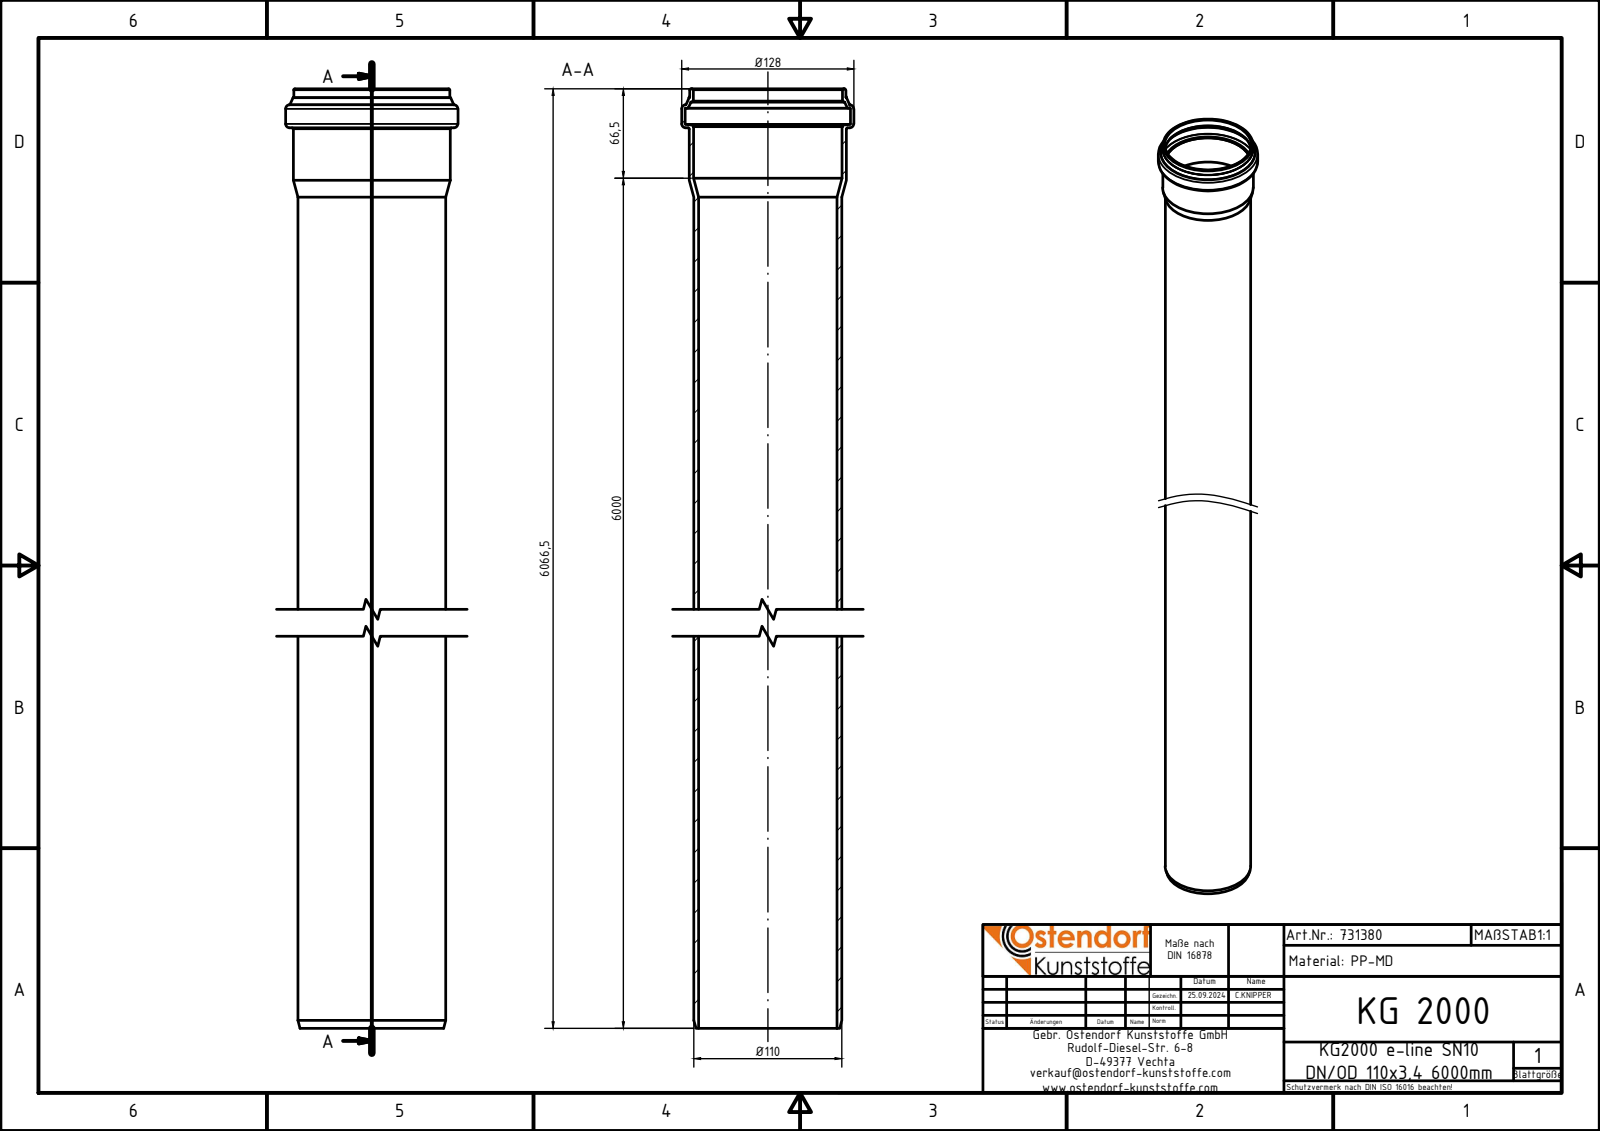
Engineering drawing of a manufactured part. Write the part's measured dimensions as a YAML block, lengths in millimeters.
part_name: "731380z"
step_written_by: "Autodesk Inventor 2024 (AUTOMOTIVE_DESIGN)"
units: millimeters
bodies: {solids: 1, faces: 36, planar: 5, cylindrical: 9, other: 22}
overall_size: [6066.5, 128, 128]
volume: 7141000
surface_area: 4071000
round_holes:
  - {diameter: 102.96, count: 1}
  - {diameter: 110.5, count: 1}
  - {diameter: 110.9, count: 1}
  - {diameter: 122.8, count: 1}
round_bosses_or_shafts:
  - {diameter: 128, count: 1}
  - {diameter: 116.7, count: 1}
  - {diameter: 116.1, count: 1}
  - {diameter: 110, count: 1}
face_to_face_distances: [6037.4, 6066.5, 29.1, 6038.22, 0.82, 28.28, 6059.85, 22.45, 21.63, 6.65]
